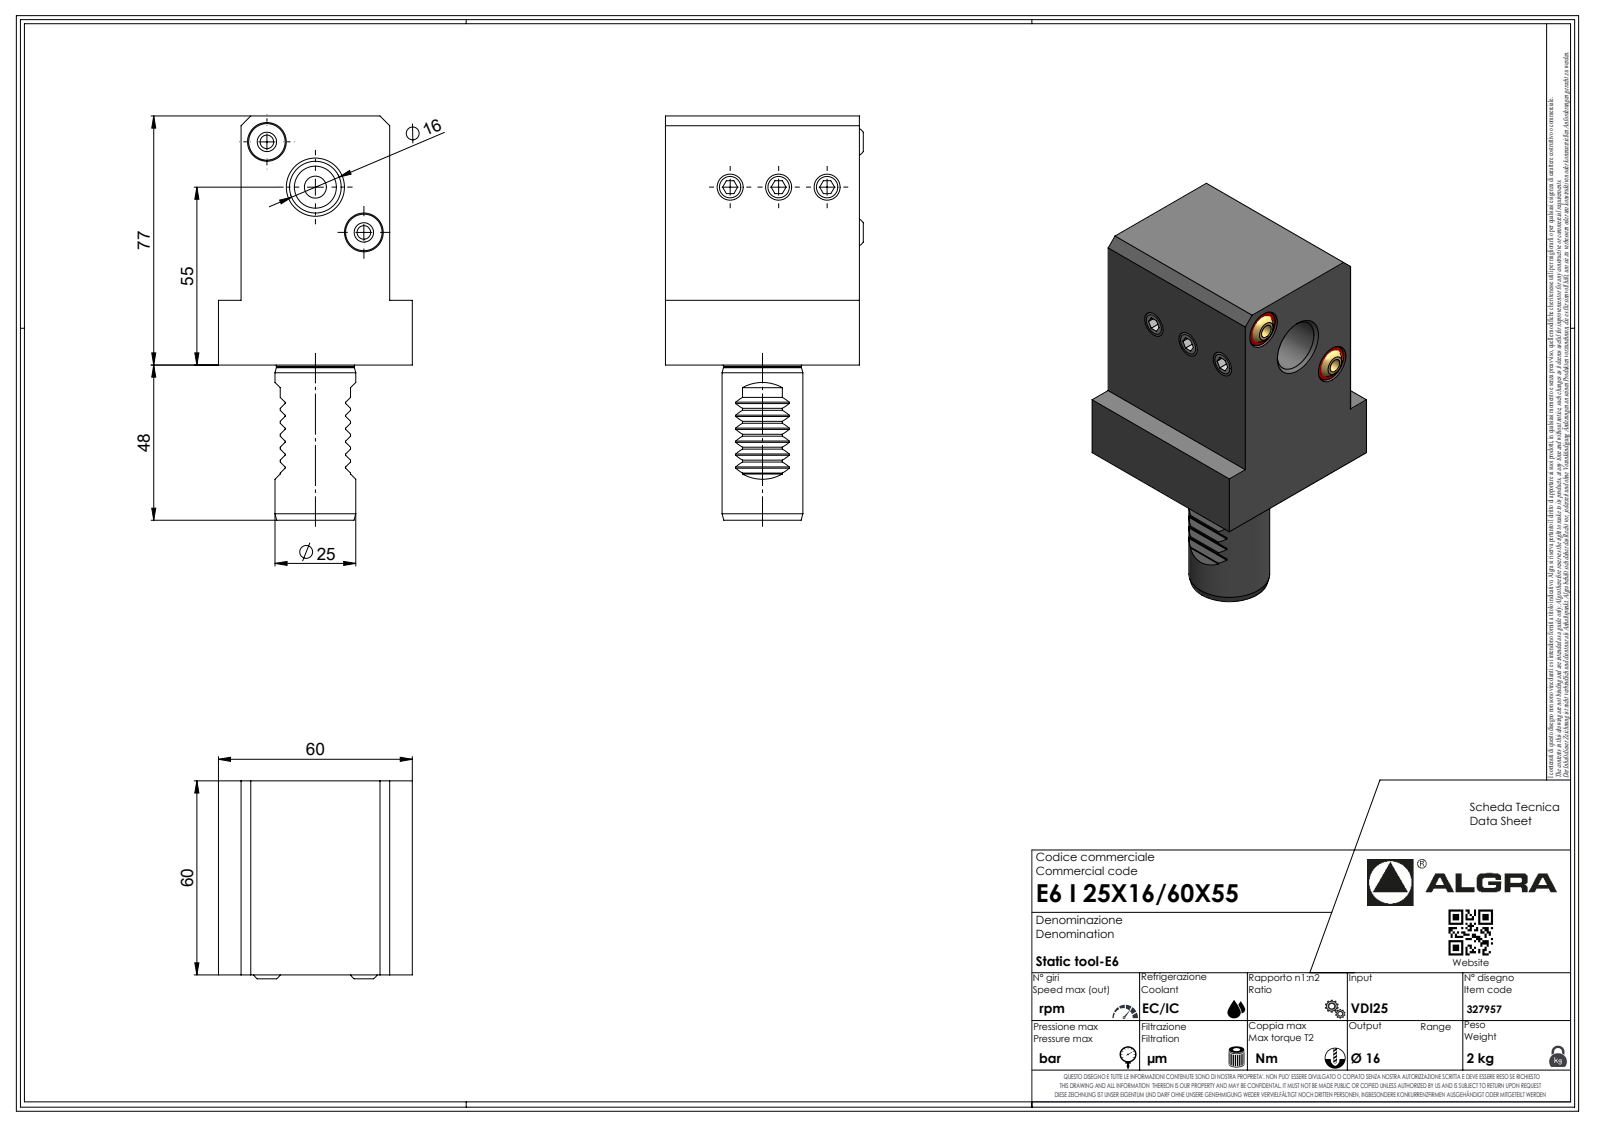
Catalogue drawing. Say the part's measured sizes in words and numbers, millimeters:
The part is named "327957". Its 3-D file was written by "SolidWorks 2023 (AUTOMOTIVE_DESIGN)". It is 1 solid with 246 faces: 162 planar, 35 cylindrical and 49 other. Overall it measures 125 by 61.2 by 60 millimeters. Its volume is 241 603 cubic millimeters and its surface area 30 366 square millimeters. Round holes: 1 of diameter 2.1, 1 of diameter 16. Round bosses or shafts: 1 of diameter 25, 1 of diameter 24.1, 1 of diameter 6.37, 1 of diameter 1.7. Partial cylindrical surfaces (rounded edges, fillets, slot ends): 7 of radius 0.33, 7 of radius 0.52, 7 of radius 3.7, 6 of radius 0.3, 1 of radius 0.21. The main face-to-face distances are 60, 46, 77, 7, 53, 20, 57, 48, 68, 125.
